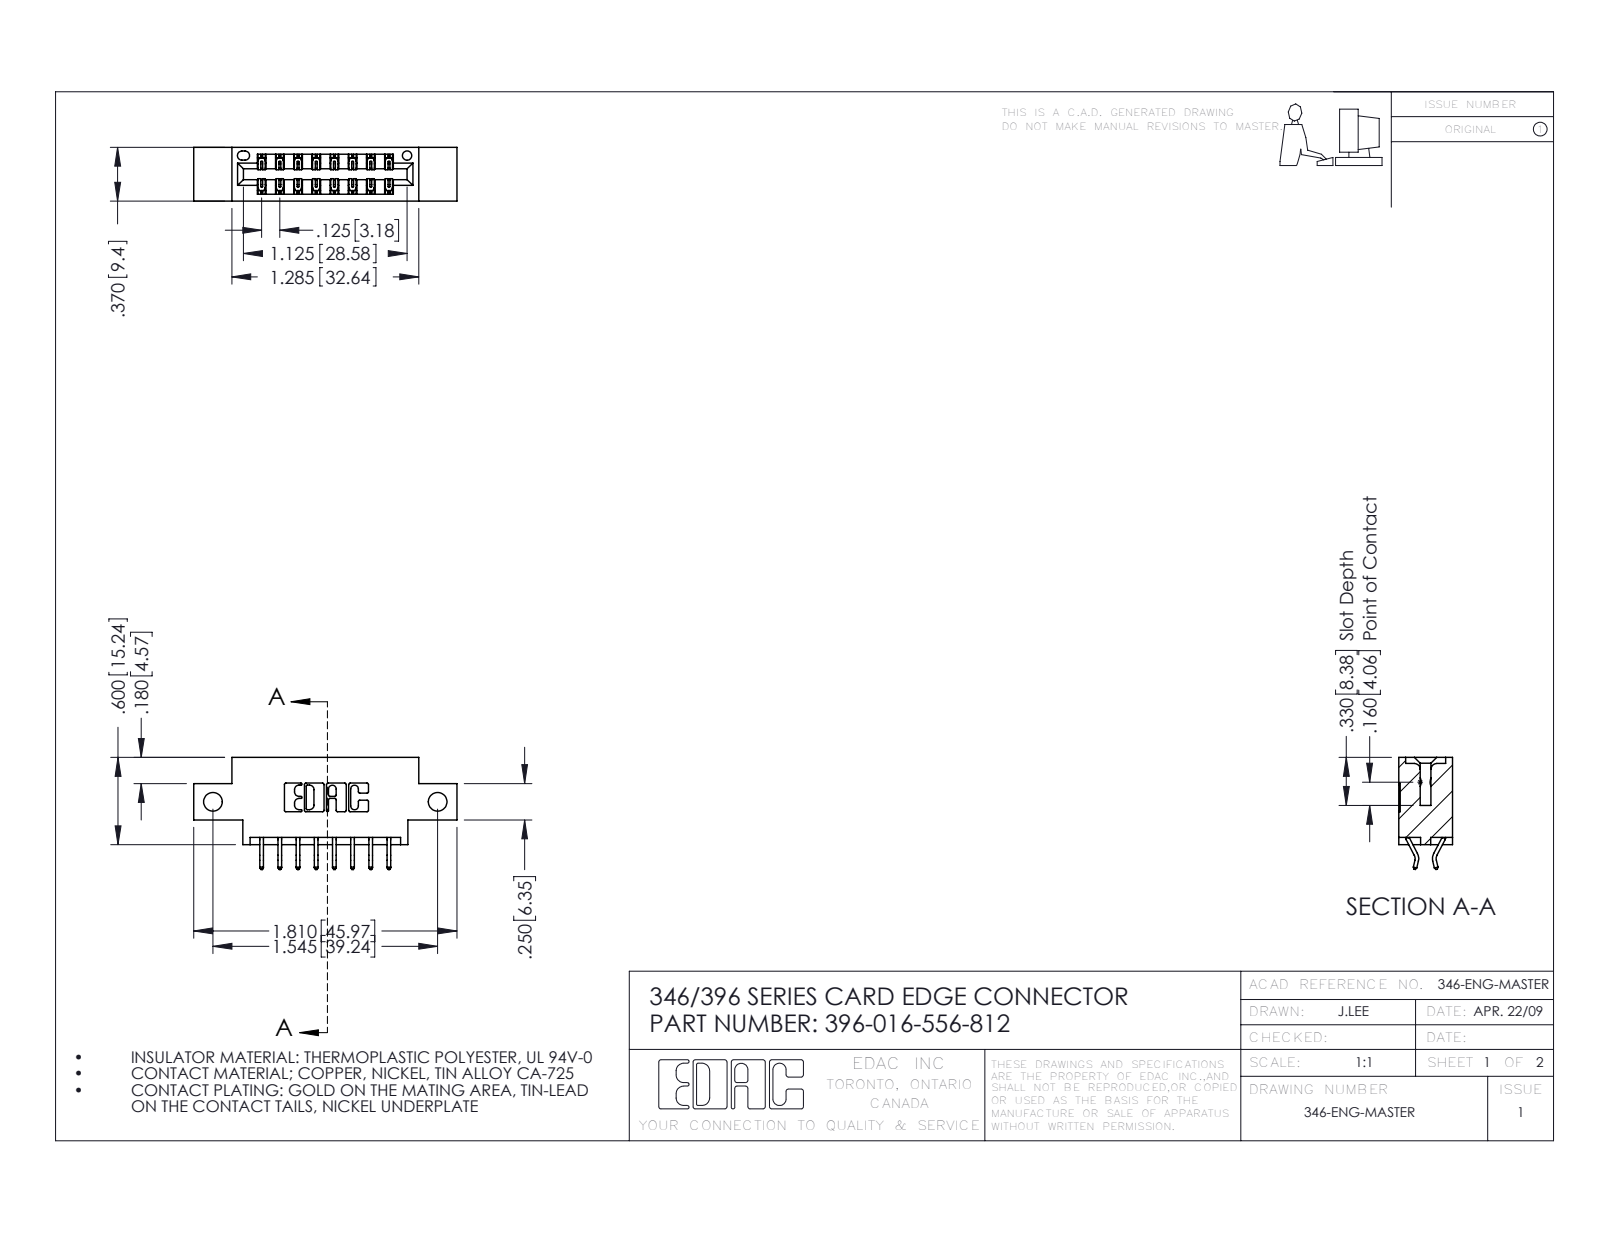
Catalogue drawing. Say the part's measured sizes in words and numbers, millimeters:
The part is named "345-292-001_556 Tail; 396-016-556-812; 346 Part_0.170 Offset - Side Mount". Its 3-D file was written by "SolidWorks 2016 (CONFIG_CONTROL_DESIGN)". It is 17 solids with 1054 faces: 704 planar, 350 cylindrical and 0 other. Overall it measures 46 by 19.6 by 9.4 millimeters. Its volume is 3 980 cubic millimeters and its surface area 4 959 square millimeters. Round holes: 2 of diameter 3.3, 1 of diameter 1.6. Partial cylindrical surfaces (rounded edges, fillets, slot ends): 24 of radius 0.2, 22 of radius 0.3, 6 of radius 0.2, 6 of radius 0.8, 3 of radius 0.7, 2 of radius 0.3, 2 of radius 0.4, 2 of radius 0.6. The main face-to-face distances are 6.4, 9.4, 1.2, 8.2, 0.6, 3.8, 5.6, 2.5, 4.4, 1.8. The hole center spacings are 39.2.
